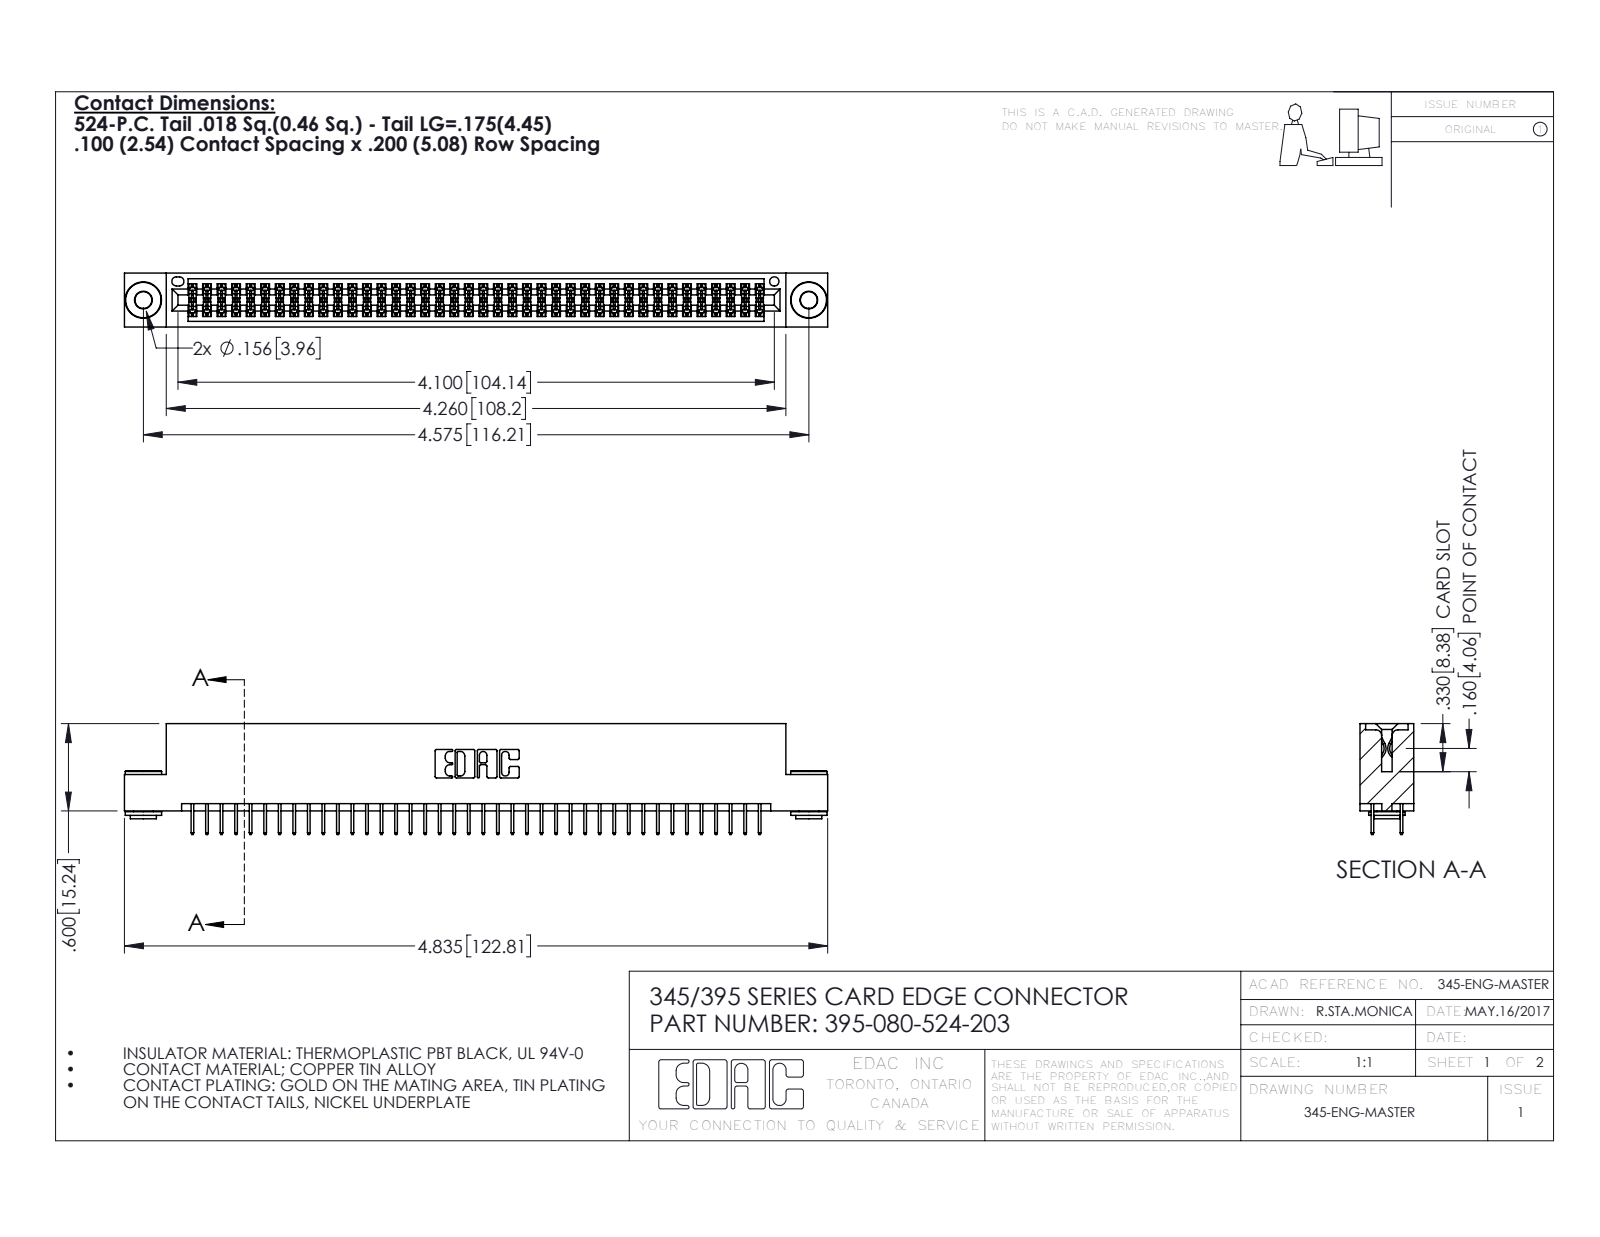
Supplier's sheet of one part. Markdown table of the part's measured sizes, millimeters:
| quantity | value |
| --- | --- |
| part name | 345-292-001_345-293-124; 345 Part_Flush Mounting Lugs - 0.156 Dia-TH; 395-080-524-203; 345-250-002_345-250-002-102 |
| STEP written by | SolidWorks 2016 (CONFIG_CONTROL_DESIGN) |
| units | millimeters |
| bodies | 83 solids, 4484 faces (3210 planar, 1266 cylindrical, 8 other) |
| overall size | 122.8 × 19.4 × 9.4 |
| volume | 11 800 mm³ |
| surface area | 17 300 mm² |
| round holes (diameter × count) | 2.9 × 2, 4 × 2, 1.6 × 1 |
| round bosses / shafts (diameter × count) | 6.4 × 2, 4.6 × 2, 3.5 × 2 |
| partial cylindrical surfaces (radius × count) | 0.2 × 120, 0.3 × 22, 0.2 × 6, 0.8 × 6, 0.7 × 3, 0.4 × 2, 0.5 × 2, 0.6 × 2 |
| main face-to-face distances | 1.8, 7.6, 5.1, 9.4, 0.6, 2.5, 6.9, 5.7, 1.8, 4.4 |
| hole center spacings | 6.9, 110.2, 116.2 |
